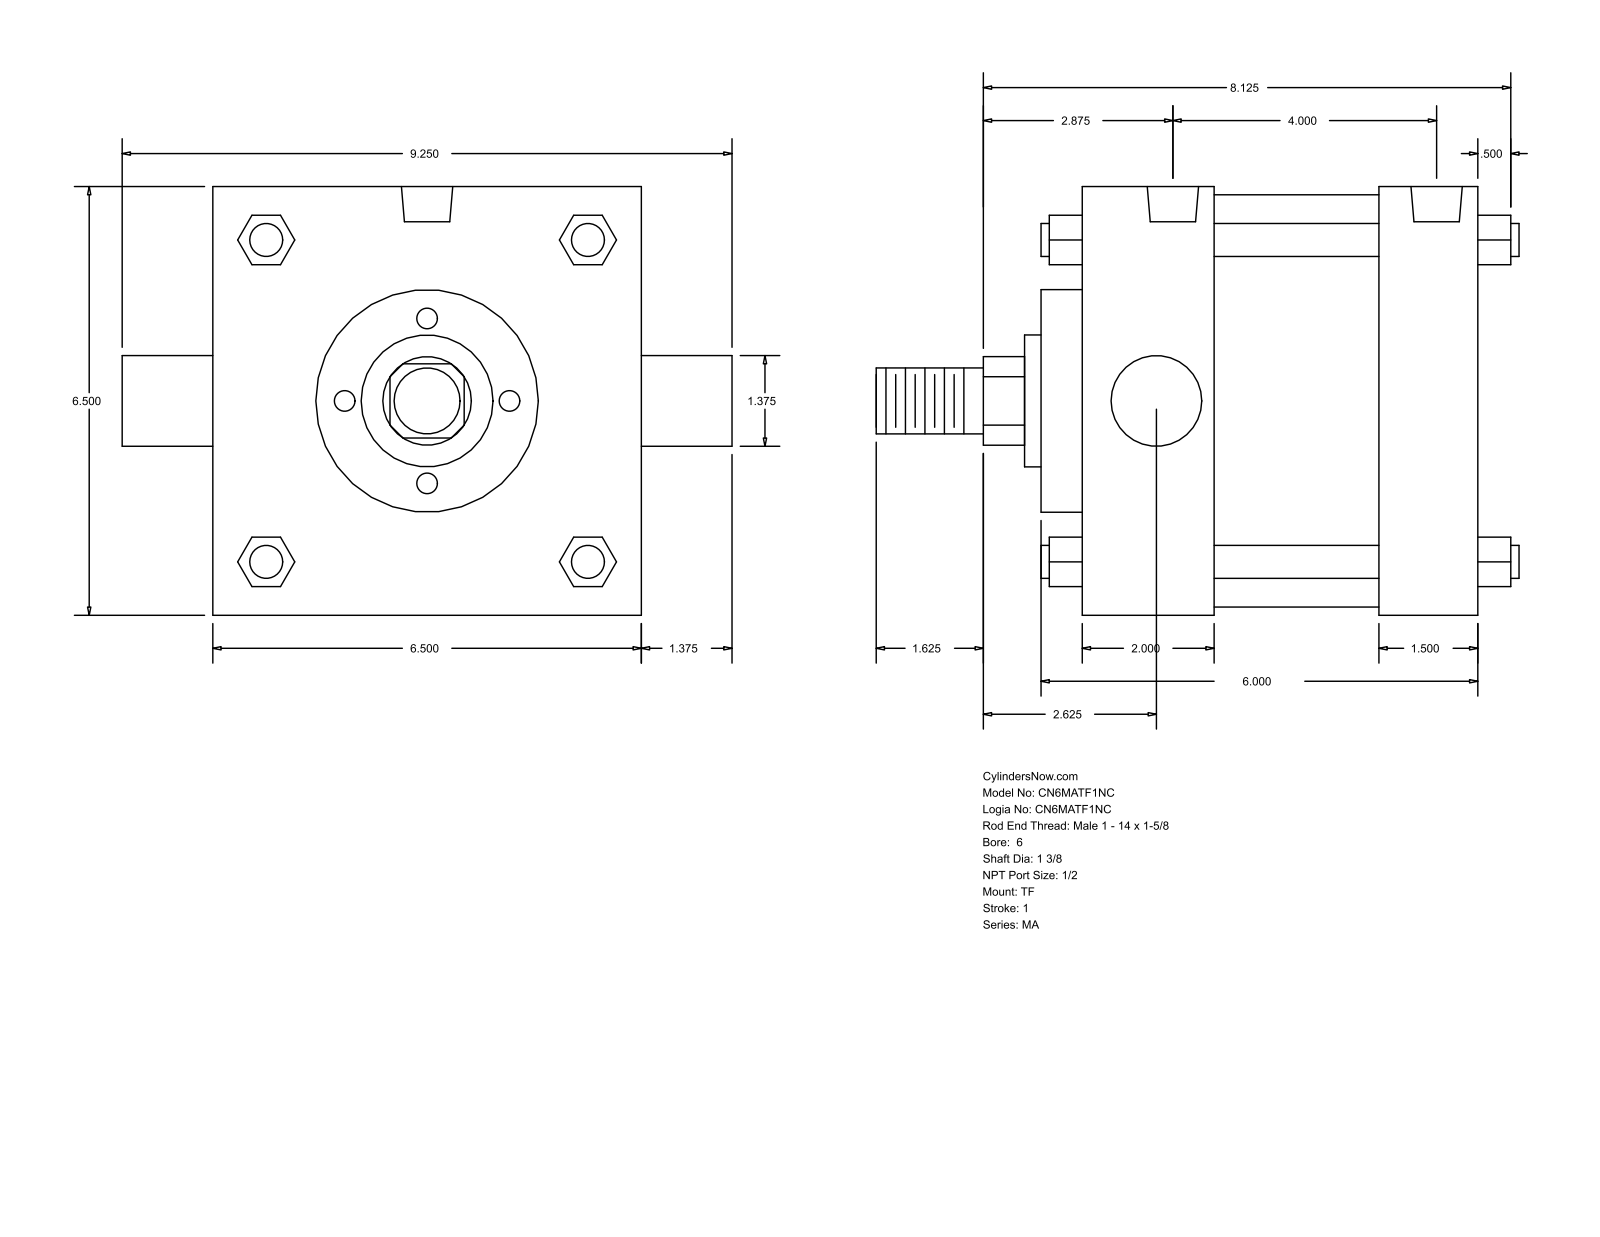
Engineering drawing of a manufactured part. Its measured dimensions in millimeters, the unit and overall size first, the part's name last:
Units: millimetres
Overall size (bounding box): 247.65 × 234.95 × 165.1
Round holes (diameter × count): ⌀17.46 ×3, ⌀19.77 ×2
Round bosses / shafts (diameter × count): ⌀12.7 ×4, ⌀34.92 ×2, ⌀158.75 ×1, ⌀85.72 ×1, ⌀50.8 ×1, ⌀25.4 ×1
Partial cylindrical surfaces — rounded edges, fillets, slot ends (radius × count): R17.06 ×1
Main face-to-face distances: 165.1, 155.58, 66.67, 50.8, 104.78, 117.47, 38.11, 15.87, 133.34, 171.45
Hole centre spacings: 3.18, 101.59, 104.77
Bodies: 0 solids, 122 faces (93 planar, 29 cylindrical, 0 other)
Part name (STEP PRODUCT): MA_TF__0600_1.375
STEP written by: GSSL Pune (CONFIG_CONTROL_DESIGN)
